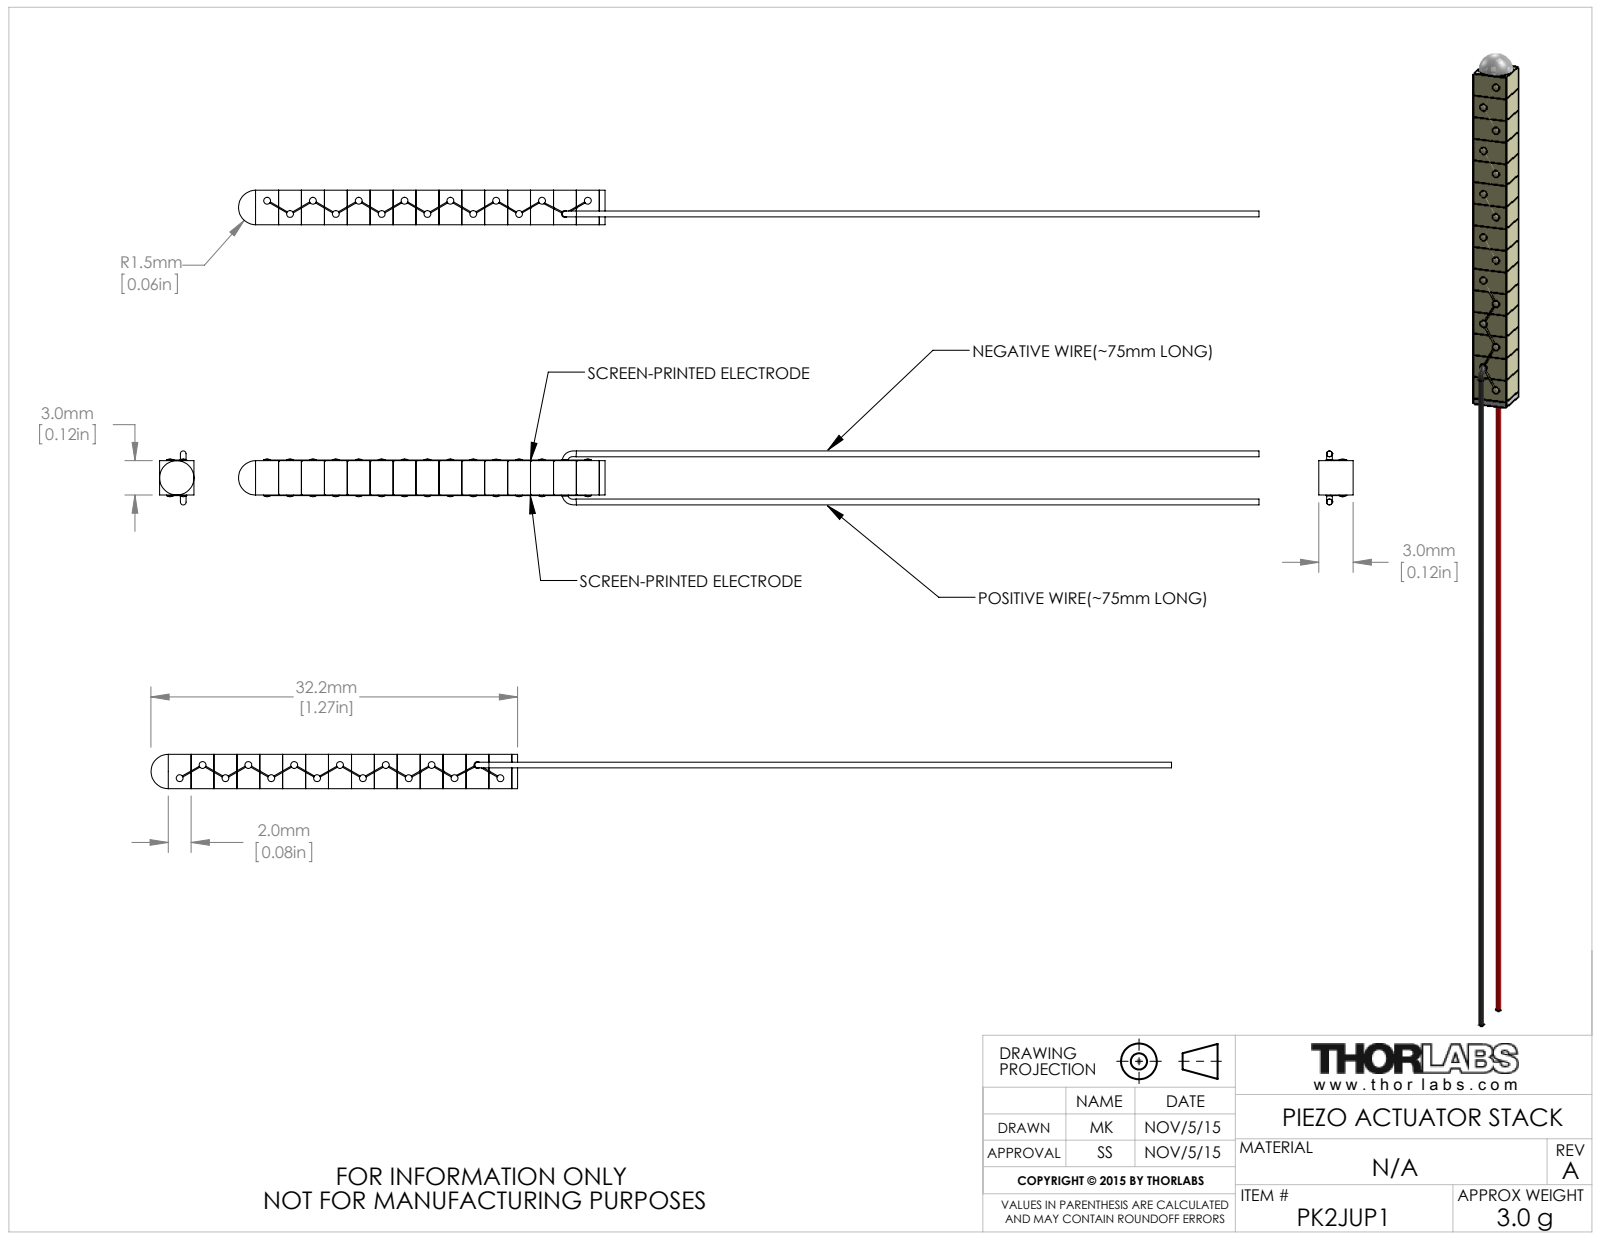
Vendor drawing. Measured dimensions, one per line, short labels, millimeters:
name: CTN003188
written by: SolidWorks 2014 (AUTOMOTIVE_DESIGN)
unit: mm
bodies: 19 solids, 312 faces (118 planar, 126 cylindrical, 68 other)
size: 89.1 × 4.72 × 3
volume: 307 mm³; area: 876 mm²
bosses: 15× ⌀0.6
face distances: 2, 4, 6, 8, 3, 10, 12, 14, 16, 18
